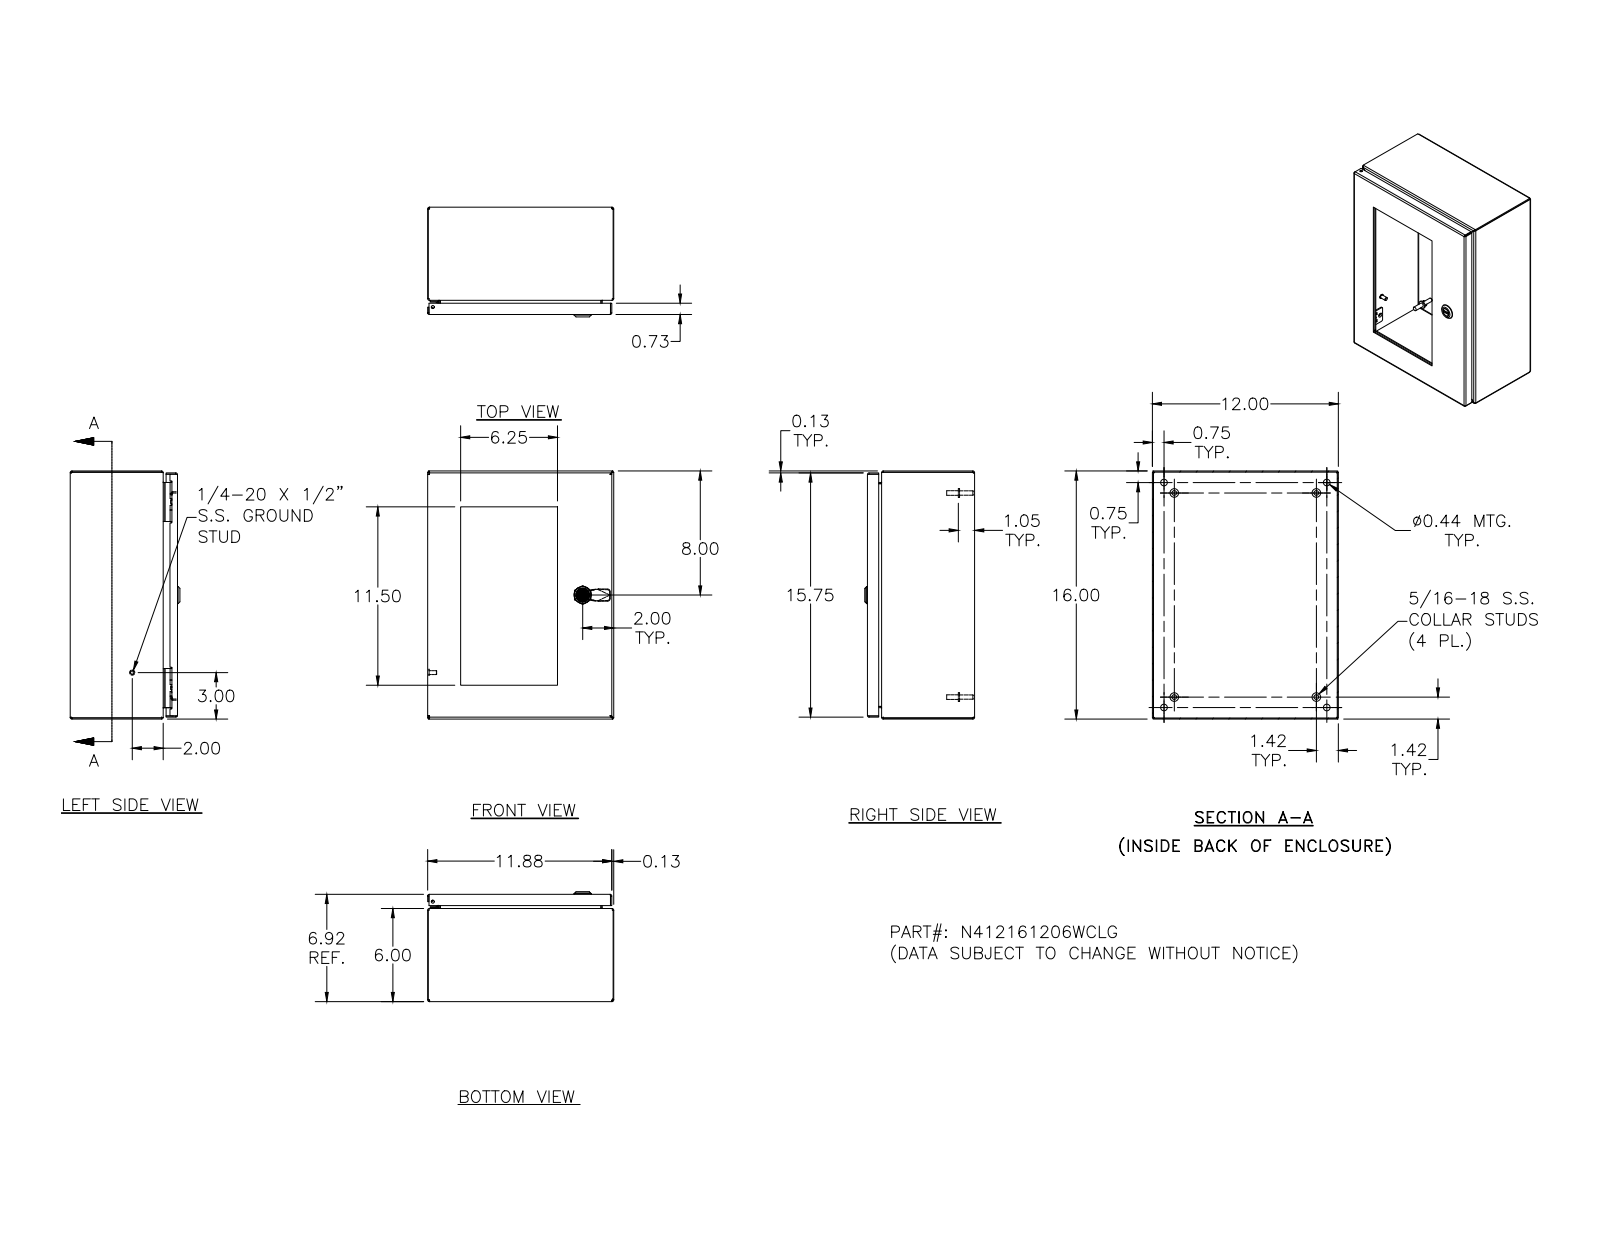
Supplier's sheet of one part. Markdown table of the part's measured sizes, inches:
| quantity | value |
| --- | --- |
| part name | N412161206WCLG |
| STEP written by | SolidWorks 2018 (AUTOMOTIVE_DESIGN) |
| units | inches |
| bodies | 57 solids, 1827 faces (687 planar, 593 cylindrical, 547 other) |
| overall size | 16 × 12 × 7.075 |
| volume | 82.94 in³ |
| surface area | 1 846 in² |
| round holes (diameter × count) | 0.156 × 12, 0.281 × 10, 0.188 × 5, 0.093 × 4, 0.152 × 4, 0.167 × 4, 0.172 × 4, 0.437 × 4, 0.187 × 1, 0.197 × 1, 0.315 × 1, 0.394 × 1 |
| round bosses / shafts (diameter × count) | 0.337 × 10, 0.25 × 10, 0.19 × 10, 0.563 × 4, 0.36 × 4, 0.32 × 4, 0.3 × 4, 0.275 × 4 |
| partial cylindrical surfaces (radius × count) | 0.031 × 34, 0.012 × 30, 0.05 × 26, 0.105 × 24, 0.016 × 18, 0.125 × 16, 0.02 × 13, 0.032 × 8 |
| main face-to-face distances | 0.074, 6.843, 6.769, 11.926, 15.926, 6.917, 12, 11.852, 0.25, 6.593 |
| hole center spacings | 4, 12, 6.221, 8.5, 8.585, 11.862, 7.5, 0.5 |
